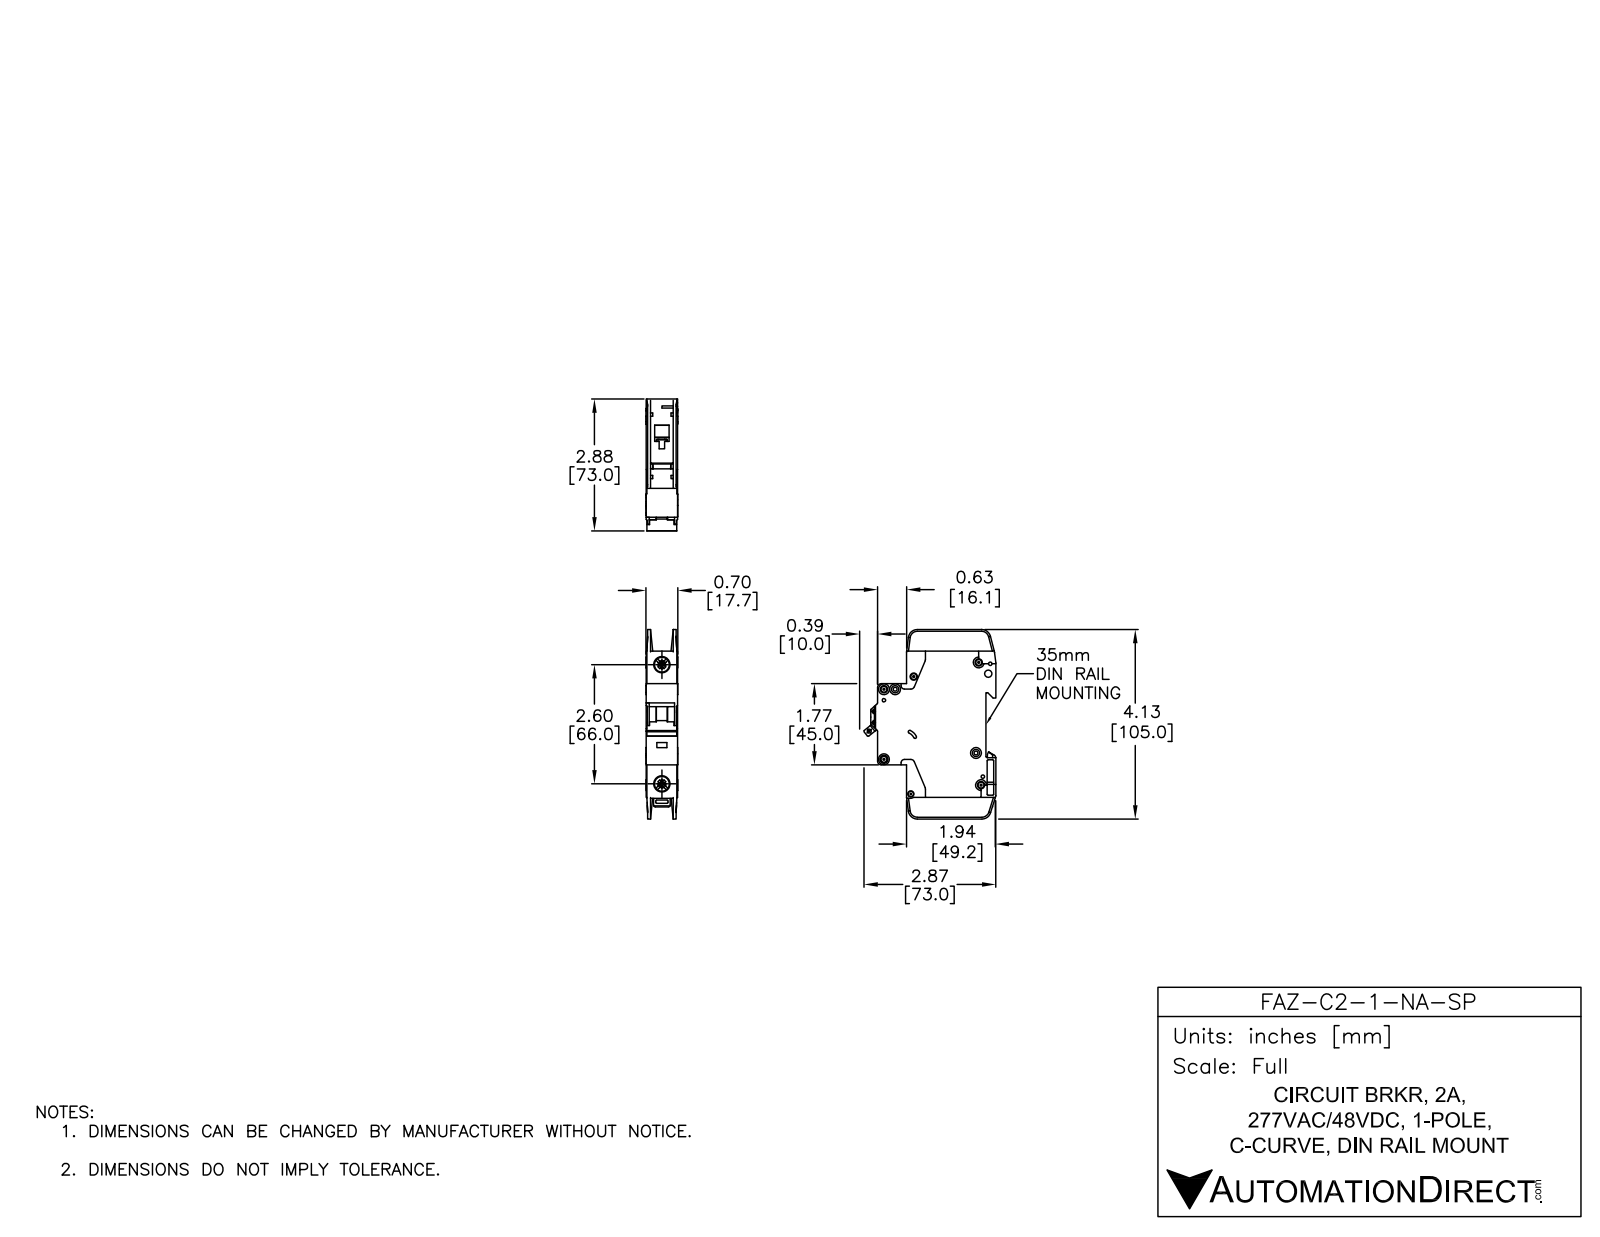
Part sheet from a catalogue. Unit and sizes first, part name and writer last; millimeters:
Units: millimetres
Overall size (bounding box): 105 × 73.04 × 17.7
Round holes (diameter × count): ⌀3.6 ×7, ⌀1.09 ×2, ⌀1.5 ×2, ⌀4 ×2, ⌀7.15 ×2, ⌀8.2 ×2, ⌀1.9 ×1, ⌀2.15 ×1, ⌀2.2 ×1, ⌀2.55 ×1, ⌀3.3 ×1, ⌀3.4 ×1
Round bosses / shafts (diameter × count): ⌀6 ×7, ⌀2.5 ×1
Partial cylindrical surfaces — rounded edges, fillets, slot ends (radius × count): R0.25 ×29, R0.5 ×18, R1 ×10, R2 ×10, R5 ×5, R4 ×4, R1.8 ×3, R0.2 ×2
Main face-to-face distances: 17.5, 15.05, 0.7, 2.45, 1.75, 15.75, 13.3, 14, 12.6, 2
Hole centre spacings: 6.2, 5.19, 6.1, 8.19, 8.56, 8.7, 11.11, 12.45
Volume: 77 695 mm³ · Surface area: 24 740 mm²
Bodies: 3 solids, 784 faces (409 planar, 263 cylindrical, 112 other)
Part name (STEP PRODUCT): FAZ-C2-1-NA-SP
STEP written by: SolidWorks 2014 (AUTOMOTIVE_DESIGN)
